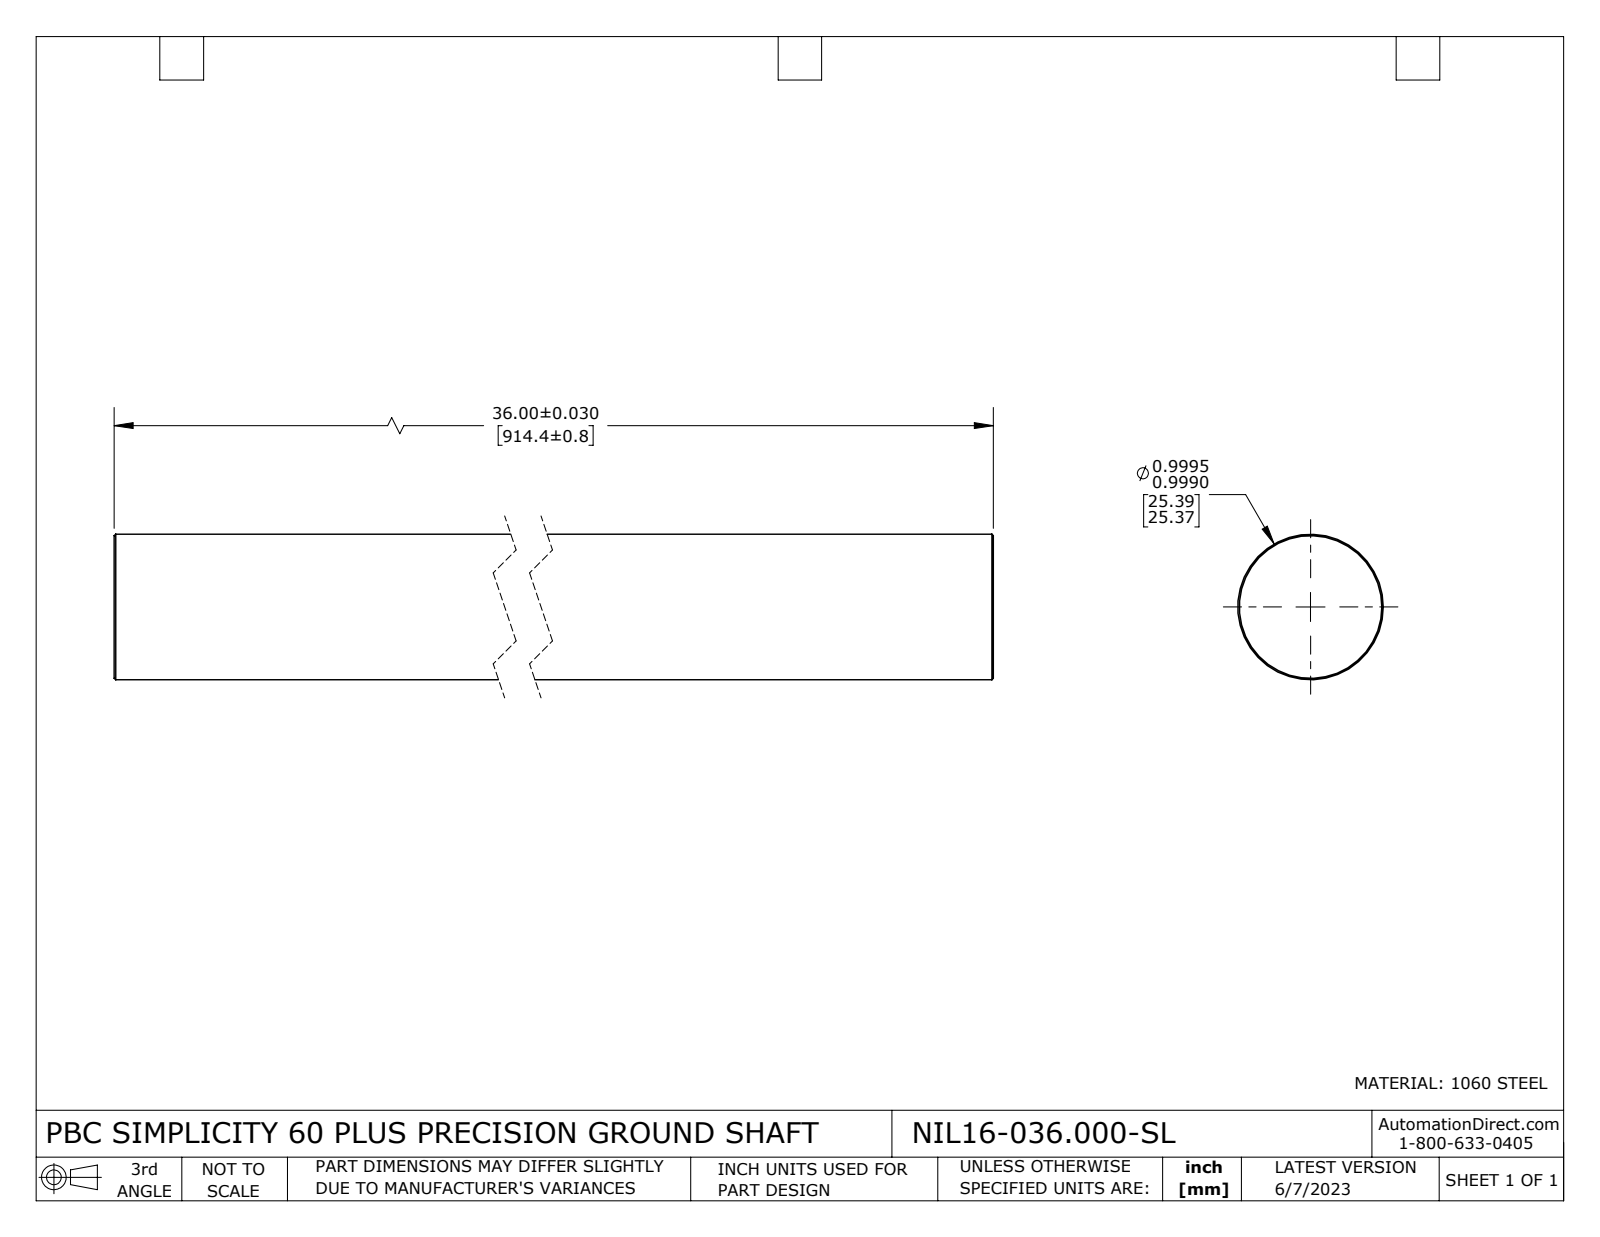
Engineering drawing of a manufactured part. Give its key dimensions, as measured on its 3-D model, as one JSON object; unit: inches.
{"part_name": "NIL16-036.000-SL", "step_written_by": "SolidWorks 2021 (CONFIG_CONTROL_DESIGN)", "units": "inches", "bodies": {"solids": 1, "faces": 8, "planar": 2, "cylindrical": 2, "other": 4}, "overall_size": [36, 1, 1], "volume_in3": 28.27, "surface_area_in2": 114.6, "round_bosses_or_shafts": [[1, 1]], "face_to_face_distances": [36]}
